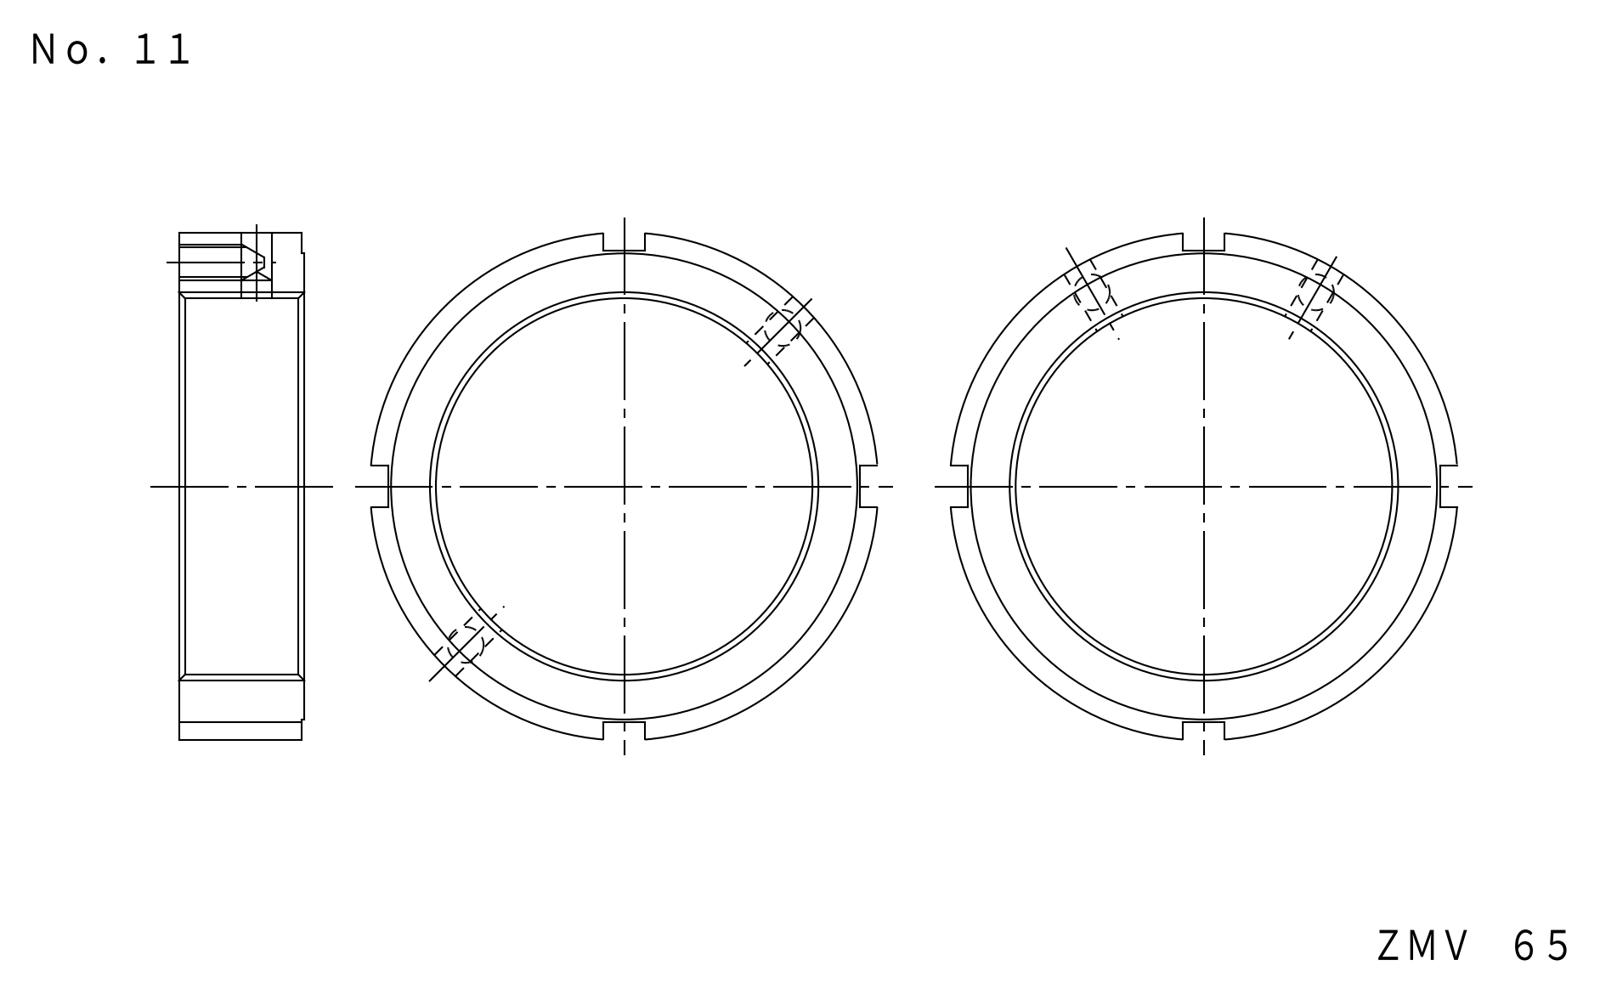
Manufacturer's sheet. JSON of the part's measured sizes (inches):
{"part_name": "FKD ZMV65", "step_written_by": "Autodesk Inventor LT (CONFIG_CONTROL_DESIGN)", "units": "inches", "bodies": {"solids": 1, "faces": 25, "planar": 15, "cylindrical": 10, "other": 0}, "overall_size": [3.335, 3.335, 0.827], "volume_in3": 2.84, "surface_area_in2": 23.87, "round_holes": [[0.194, 2], [0.197, 2], [2.559, 1]], "round_bosses_or_shafts": [[3.346, 1], [3.071, 1]], "face_to_face_distances": [0.827, 0.02, 0.807, 1.417, 1.693, 3.11, 0.276], "hole_center_spacings": [1.476, 2.953]}
